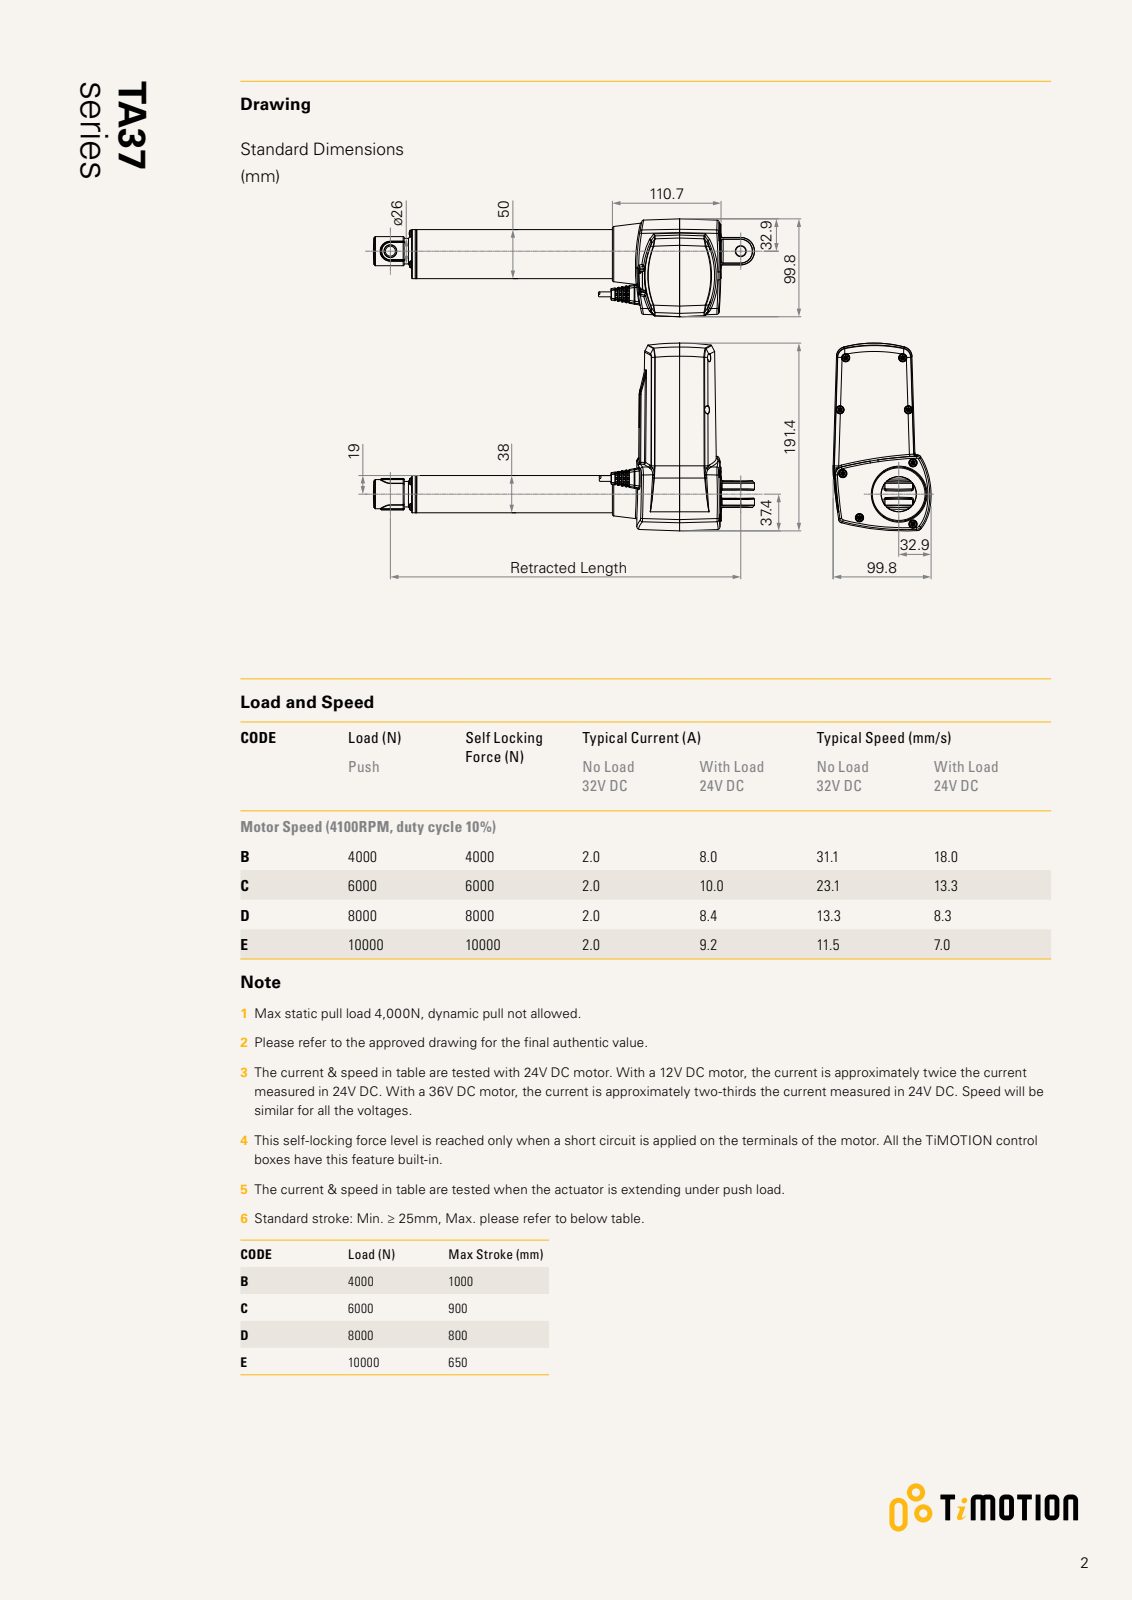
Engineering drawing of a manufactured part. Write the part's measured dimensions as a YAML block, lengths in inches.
part_name: "三維零件圖-套管-0; 三維零件圖-40510-154-SR-A; 三維零件圖-31501-116-齒輪箱體-A; 三維零件圖-31605-761-外殼左蓋-B (+8 more)"
step_written_by: "SolidWorks 2015 (CONFIG_CONTROL_DESIGN)"
units: inches
bodies: {solids: 22, faces: 5343, planar: 1338, cylindrical: 1658, other: 2347}
overall_size: [14.199, 7.537, 3.929]
volume: 28.47
surface_area: 593.7
round_holes:
  - {diameter: 0.059, count: 17}
  - {diameter: 0.13, count: 8}
  - {diameter: 0.165, count: 7}
  - {diameter: 0.205, count: 7}
  - {diameter: 0.159, count: 3}
  - {diameter: 0.157, count: 2}
  - {diameter: 0.402, count: 2}
  - {diameter: 0.394, count: 1}
  - {diameter: 0.492, count: 1}
  - {diameter: 0.551, count: 1}
  - {diameter: 0.787, count: 1}
  - {diameter: 0.827, count: 1}
round_bosses_or_shafts:
  - {diameter: 0.287, count: 8}
  - {diameter: 0.157, count: 8}
  - {diameter: 0.093, count: 8}
  - {diameter: 0.295, count: 6}
  - {diameter: 0.268, count: 3}
  - {diameter: 0.154, count: 3}
  - {diameter: 2.362, count: 1}
  - {diameter: 1.22, count: 1}
partial_cylinders:
  - {radius: 0.012, count: 132}
  - {radius: 0.02, count: 77}
  - {radius: 0.008, count: 47}
  - {radius: 0.016, count: 34}
  - {radius: 0.039, count: 32}
  - {radius: 0.059, count: 8}
  - {radius: 0.197, count: 8}
  - {radius: 0.177, count: 7}
face_to_face_distances: [0.118, 0.059, 0.055, 0.709, 0.354, 1.063, 0.039, 0.551, 0.285, 0.236]
hole_center_spacings: [0.827, 1.615, 0.428, 0.827, 0.906, 2.283, 0.185, 0.404]
